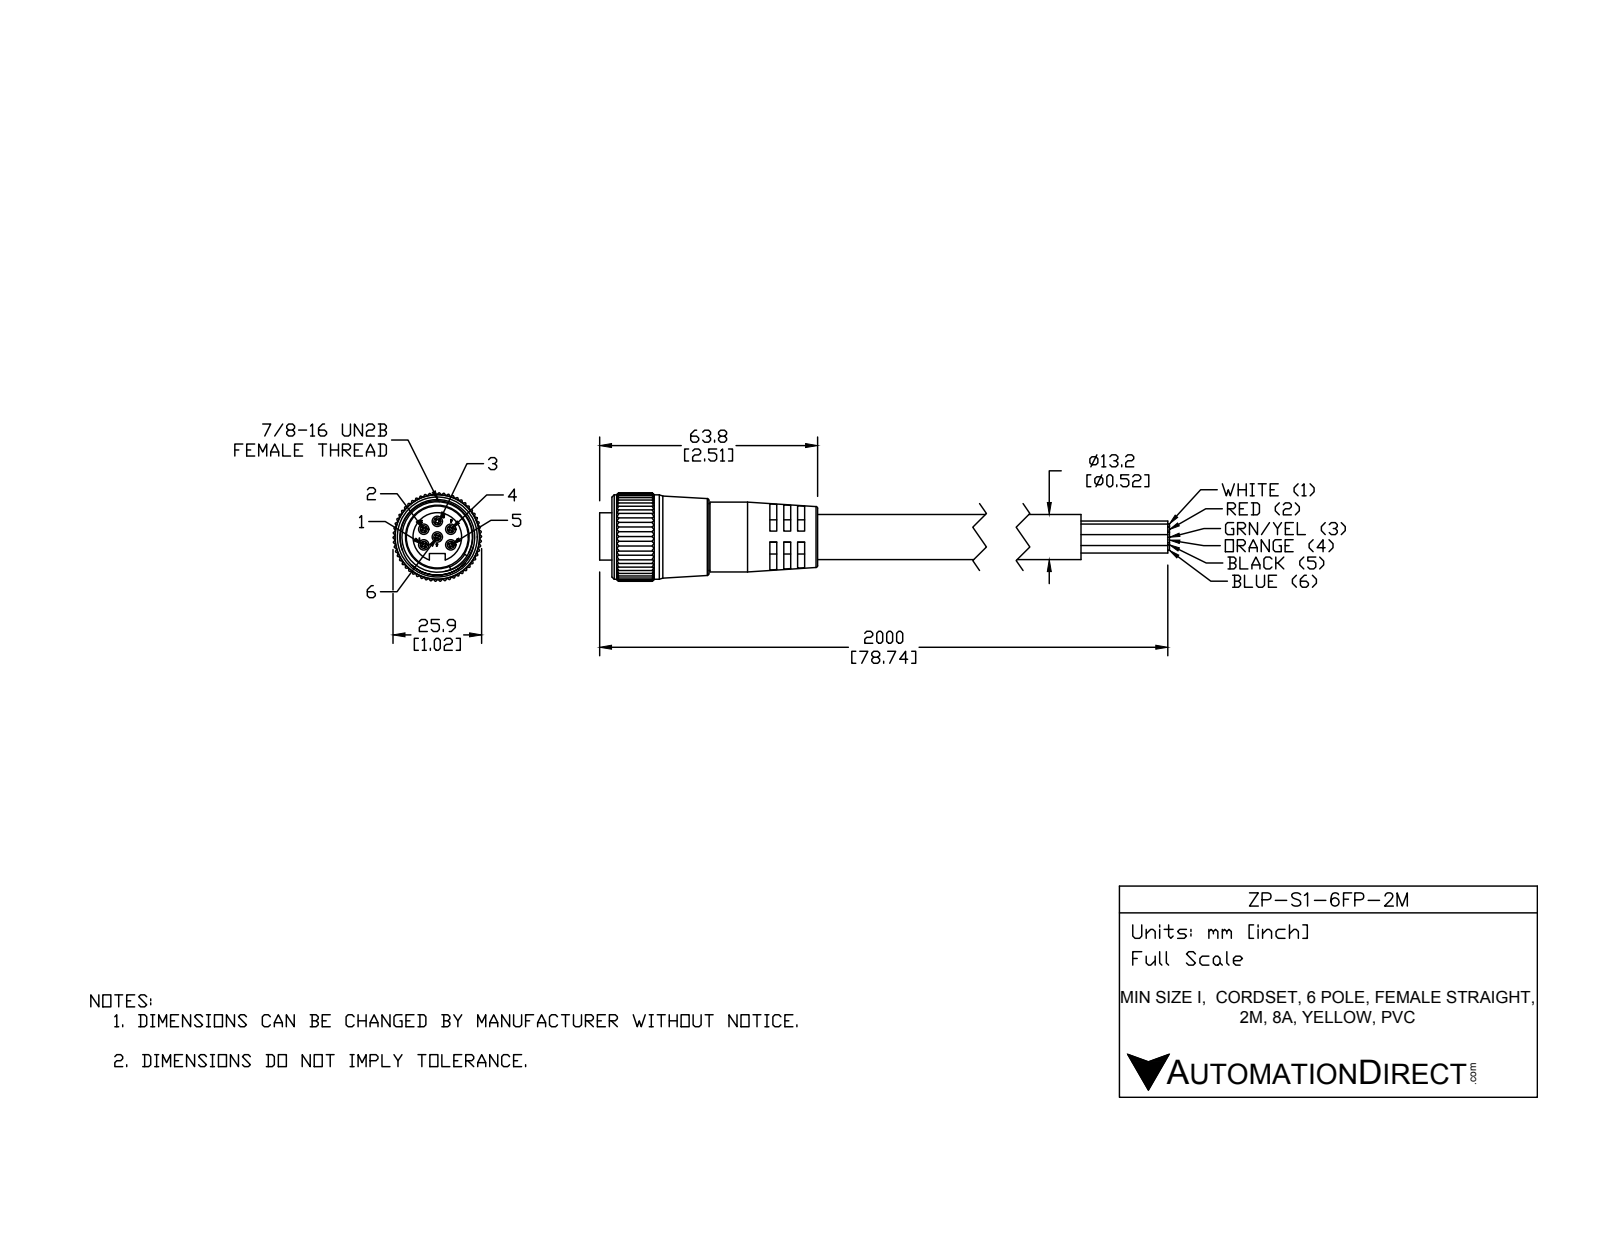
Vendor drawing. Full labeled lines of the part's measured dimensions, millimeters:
Part name (STEP PRODUCT): ZP-S1-6FP-2M
STEP written by: SolidWorks 2015 (AUTOMOTIVE_DESIGN)
Units: millimetres
Bodies: 2 solids, 593 faces (222 planar, 312 cylindrical, 59 other)
Overall size (bounding box): 110.36 × 52.91 × 25.84
Volume: 31 008 mm³ · Surface area: 12 592 mm²
Round holes (diameter × count): ⌀3.05 ×6, ⌀18.14 ×1, ⌀20.58 ×1, ⌀21 ×1
Round bosses / shafts (diameter × count): ⌀13.21 ×2, ⌀24.68 ×1, ⌀20.4 ×1, ⌀19.5 ×1, ⌀14.22 ×1
Partial cylindrical surfaces — rounded edges, fillets, slot ends (radius × count): R0.25 ×165, R5.25 ×1, R12.93 ×1
Main face-to-face distances: 4.03, 2, 2.03, 6.03, 8.06, 6.06, 21.13, 23.13, 25.16, 27.16
Hole centre spacings: 4.57, 7.92, 4.58, 9.15
